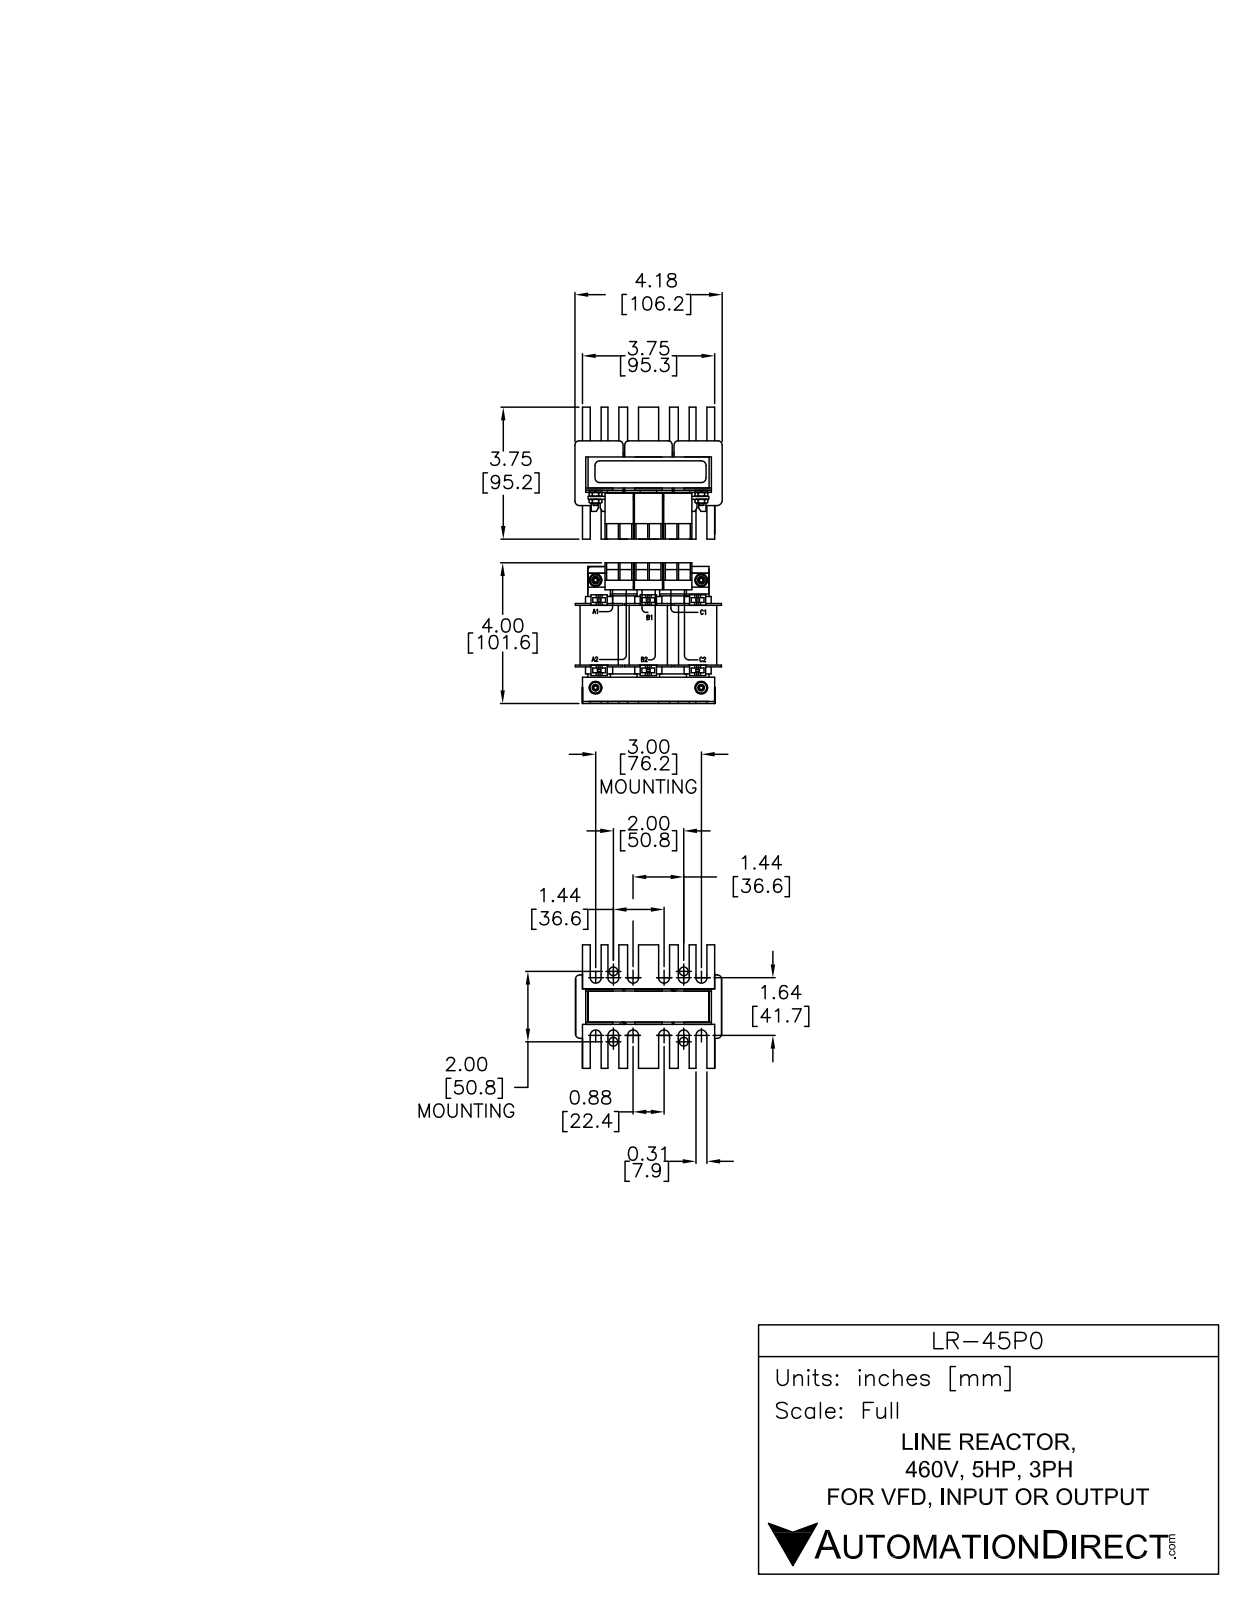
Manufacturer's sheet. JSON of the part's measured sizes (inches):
{"part_name": "LR-45P0", "step_written_by": "SolidWorks 2011 (AUTOMOTIVE_DESIGN)", "units": "inches", "bodies": {"solids": 17, "faces": 941, "planar": 743, "cylindrical": 198, "other": 0}, "overall_size": [4.144, 3.874, 3.514], "volume_in3": 16.62, "surface_area_in2": 153.8, "round_bosses_or_shafts": [[0.305, 4], [0.138, 4]], "partial_cylinders_radius": [[0.157, 50], [0.072, 24], [0.315, 12], [0.118, 6], [0.034, 3], [0.049, 2]], "face_to_face_distances": [0.197, 0.846, 0.108, 2.008, 1.033, 1.043, 0.295, 1.142, 2.795, 0.098]}
